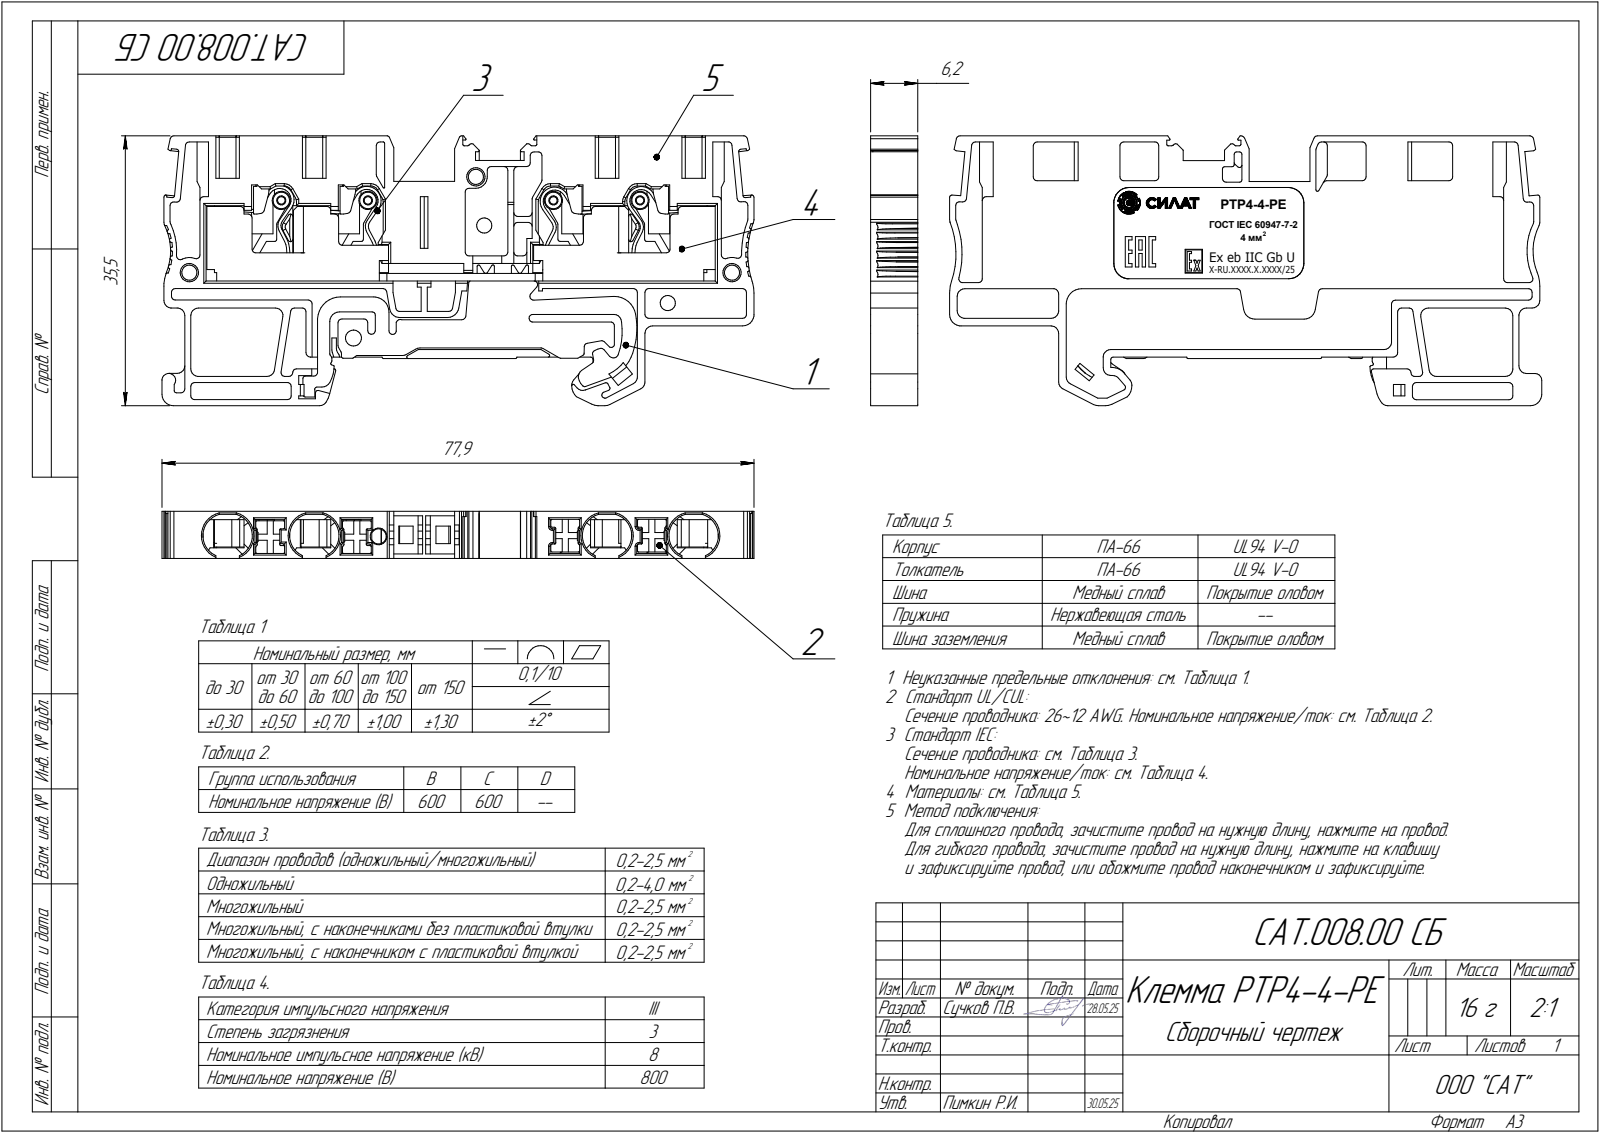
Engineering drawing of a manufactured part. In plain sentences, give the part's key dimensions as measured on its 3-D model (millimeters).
The part is named "Клемма PTP4-4-PE". Its 3-D file was written by "SolidWorks 2024 (AUTOMOTIVE_DESIGN)". It is 1 solid with 476 faces: 322 planar, 144 cylindrical and 10 other. Overall it measures 77.9 by 35.5 by 6.2 millimeters. Its volume is 12 643 cubic millimeters and its surface area 6 756 square millimeters. Round holes: 1 of diameter 2.1. Partial cylindrical surfaces (rounded edges, fillets, slot ends): 43 of radius 0.5, 38 of radius 0.3, 12 of radius 1, 8 of radius 2.9, 6 of radius 0.15, 6 of radius 0.2, 3 of radius 1.5, 2 of radius 0.1. The main face-to-face distances are 6.2, 29.3, 2.35, 35.5, 6.65, 31.32, 25.12, 4.18, 4.3, 2.75.
